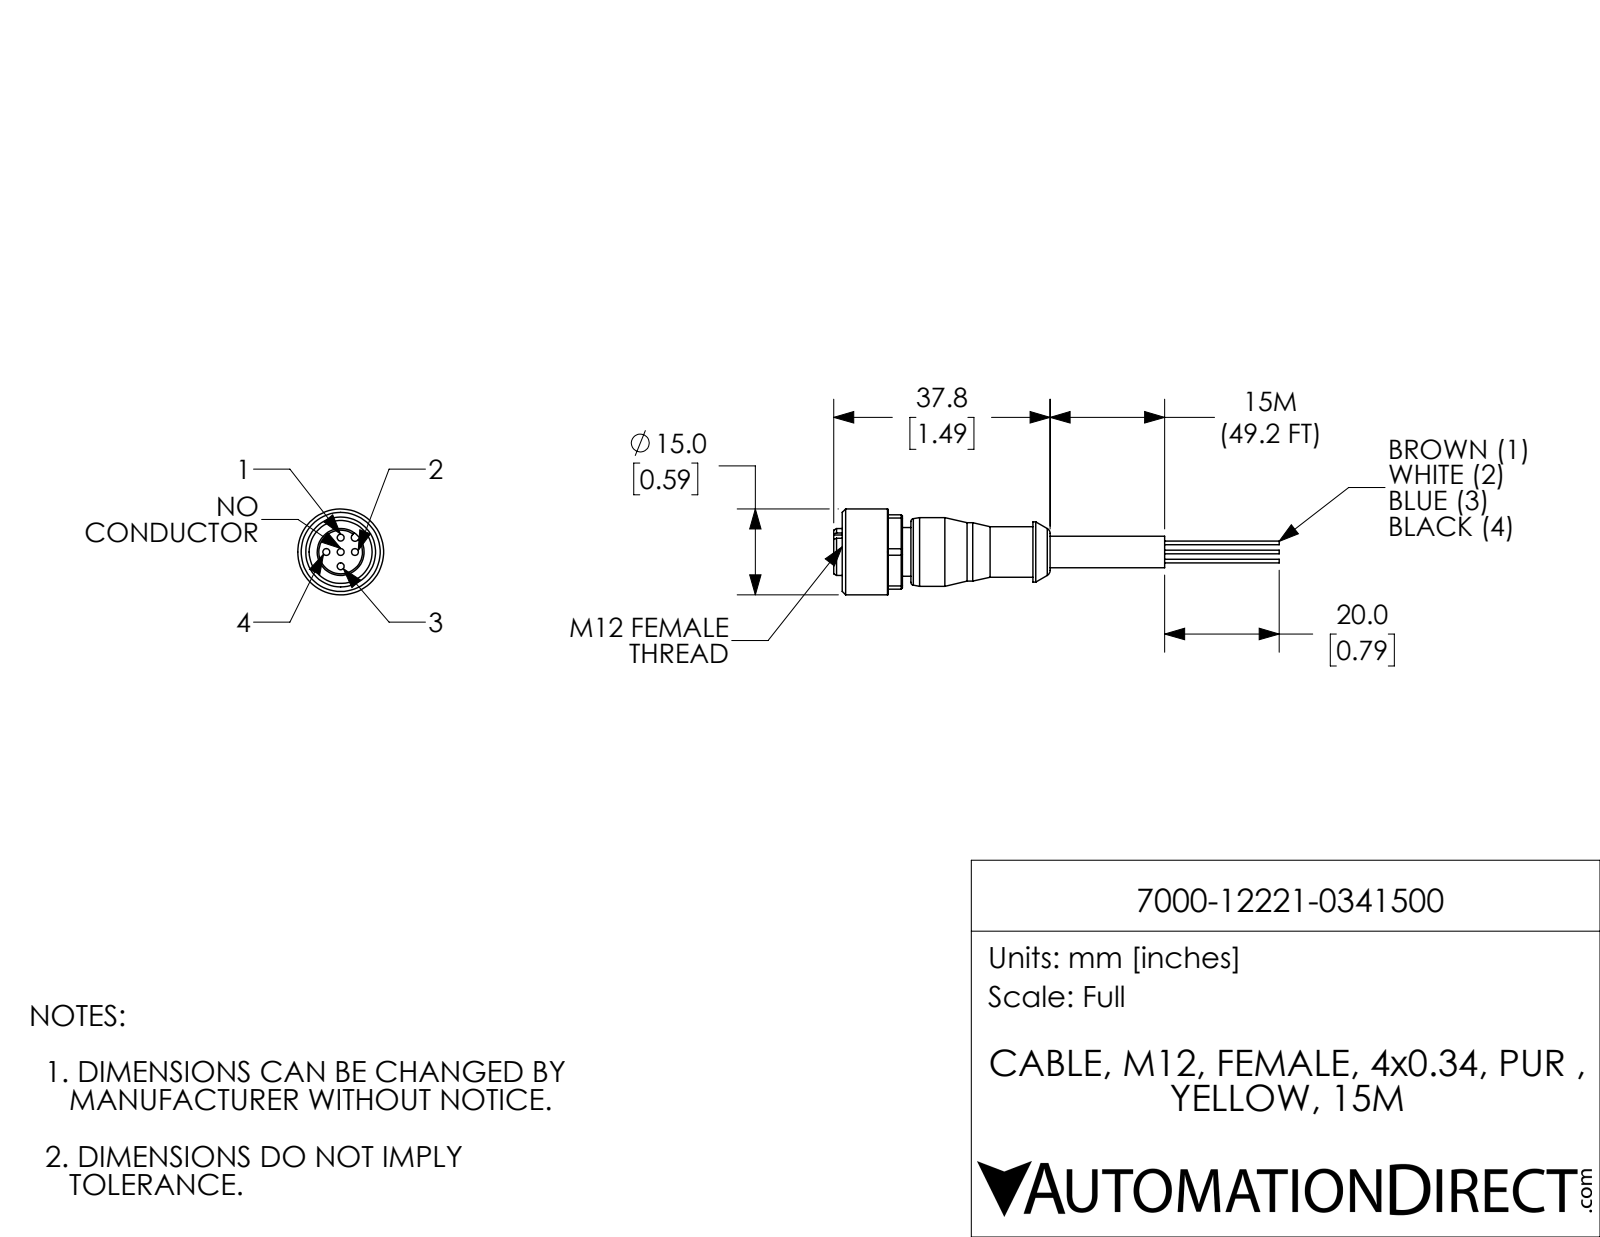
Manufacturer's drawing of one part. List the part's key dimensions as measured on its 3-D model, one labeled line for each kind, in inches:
Part name (STEP PRODUCT): 7000-12221-0341500
STEP written by: SolidWorks 2021 (CONFIG_CONTROL_DESIGN)
Units: inches
Bodies: 1 solid, 103 faces (33 planar, 43 cylindrical, 27 other)
Overall size (bounding box): 3.063 × 0.591 × 0.591
Volume: 0.247 in³ · Surface area: 4.386 in²
Round holes (diameter × count): ⌀0.047 ×5, ⌀0.433 ×1
Round bosses / shafts (diameter × count): ⌀0.026 ×4, ⌀0.591 ×1, ⌀0.472 ×1, ⌀0.413 ×1, ⌀0.402 ×1, ⌀0.346 ×1, ⌀0.335 ×1, ⌀0.323 ×1
Partial cylindrical surfaces — rounded edges, fillets, slot ends (radius × count): R0.026 ×1, R0.283 ×1
Main face-to-face distances: 0.472, 0.059, 0.118, 0.512, 0.354, 1.016, 0.295, 0.413, 0.098, 0.531
Hole centre spacings: 0.098, 0.139, 0.197
